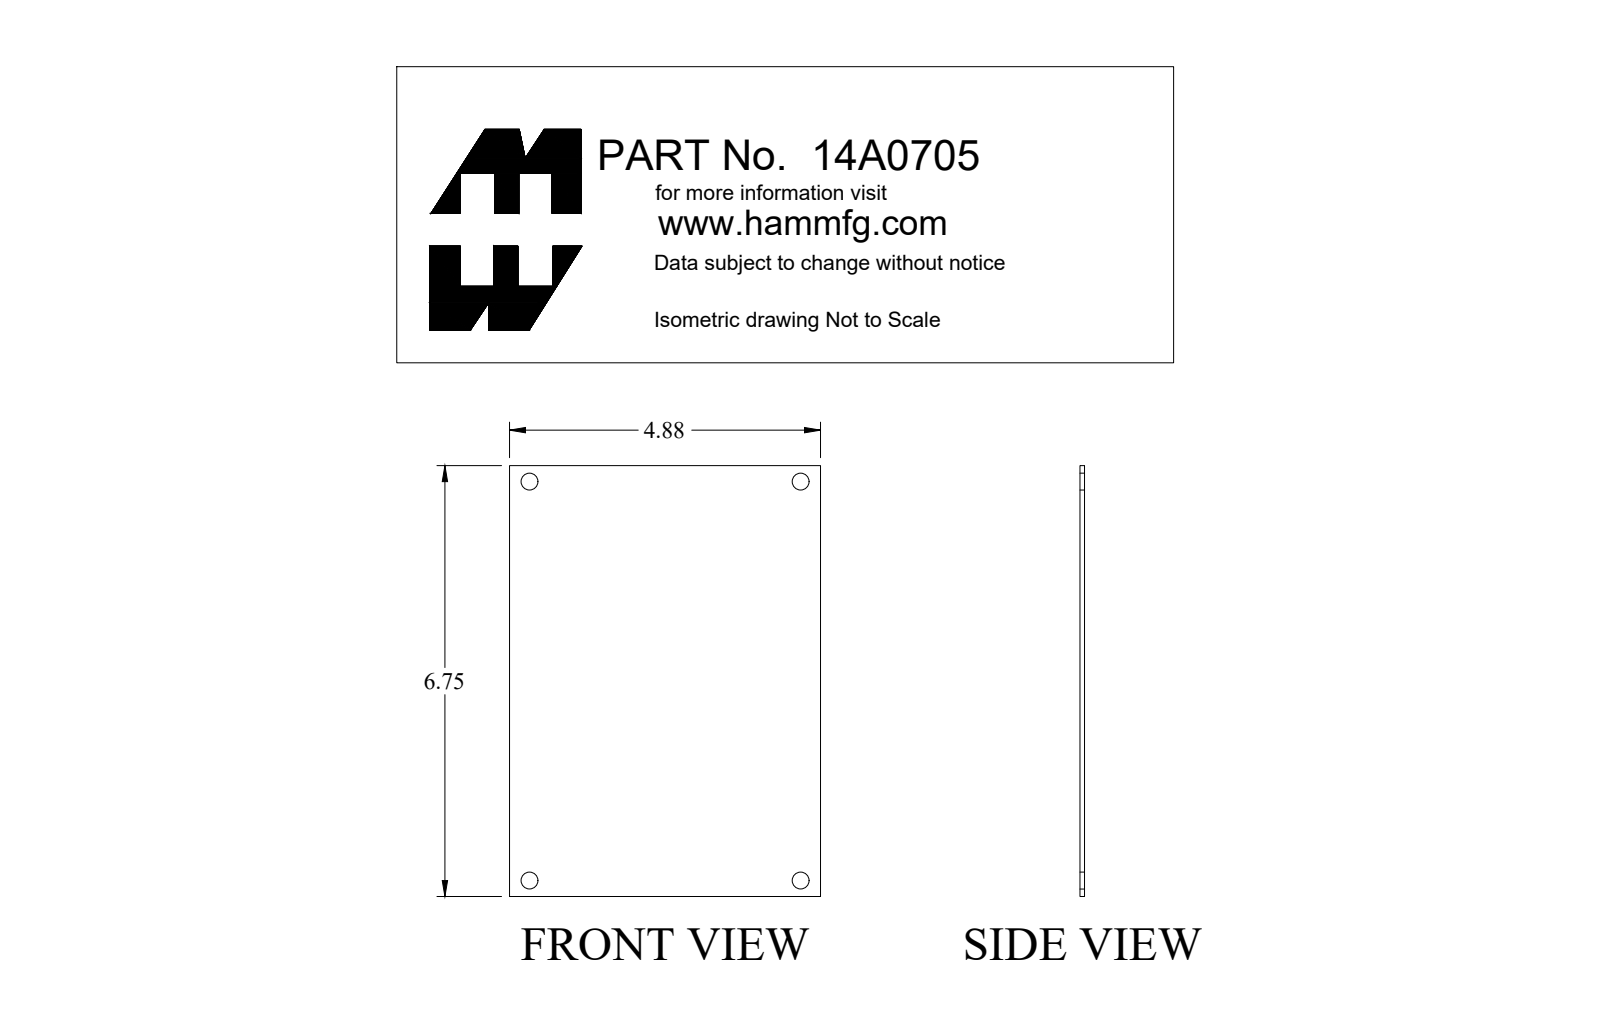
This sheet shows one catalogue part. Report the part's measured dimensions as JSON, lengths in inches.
{"part_name": "14A0705", "step_written_by": "SolidWorks 2018 (AUTOMOTIVE_DESIGN)", "units": "inches", "bodies": {"solids": 1, "faces": 10, "planar": 6, "cylindrical": 4, "other": 0}, "overall_size": [6.75, 4.875, 0.072], "volume_in3": 2.353, "surface_area_in2": 67.29, "round_holes": [[0.265, 4]], "face_to_face_distances": [0.072, 4.875, 6.75], "hole_center_spacings": [4.25, 6.25, 7.558]}
